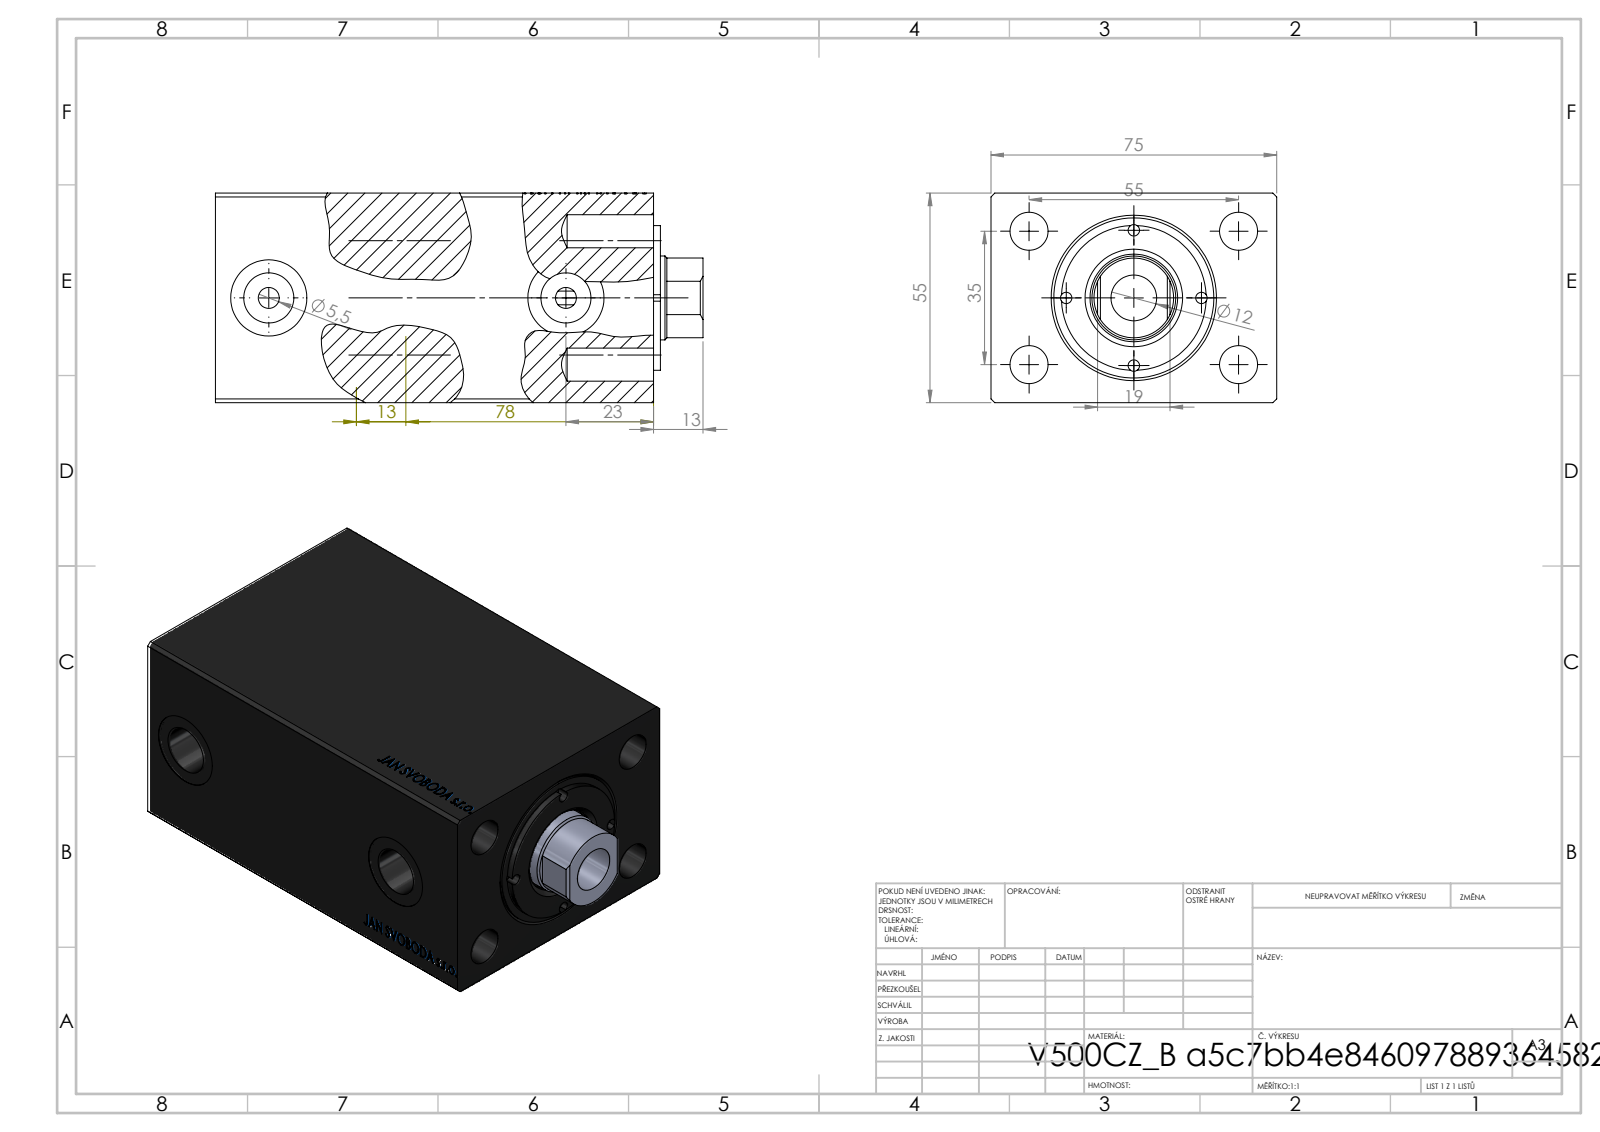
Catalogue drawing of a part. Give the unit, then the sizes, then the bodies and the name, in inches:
Units: inches
Overall size (bounding box): 5.039 × 2.953 × 2.165
Round holes (diameter × count): ⌀0.118 ×4, ⌀0.394 ×4, ⌀0.217 ×2, ⌀0.518 ×2, ⌀0.787 ×2, ⌀0.472 ×1, ⌀0.866 ×1, ⌀0.906 ×1, ⌀1.26 ×1, ⌀1.417 ×1, ⌀1.654 ×1
Round bosses / shafts (diameter × count): ⌀1.496 ×1
Partial cylindrical surfaces — rounded edges, fillets, slot ends (radius × count): R0.412 ×1
Main face-to-face distances: 2.165, 2.953, 4.528, 3.346, 1.181, 0.394, 4.134, 4.52, 4.126, 1.173
Hole centre spacings: 0.699, 0.789, 0.988, 1.083, 1.283, 1.76, 1.91, 1.378
Volume: 26.67 in³ · Surface area: 105.9 in²
Bodies: 3 solids, 873 faces (402 planar, 61 cylindrical, 410 other)
Part name (STEP PRODUCT): V500CZ; V500CZ_vnitrni_cast_vysunovaci
STEP written by: SolidWorks 2019 (CONFIG_CONTROL_DESIGN)
